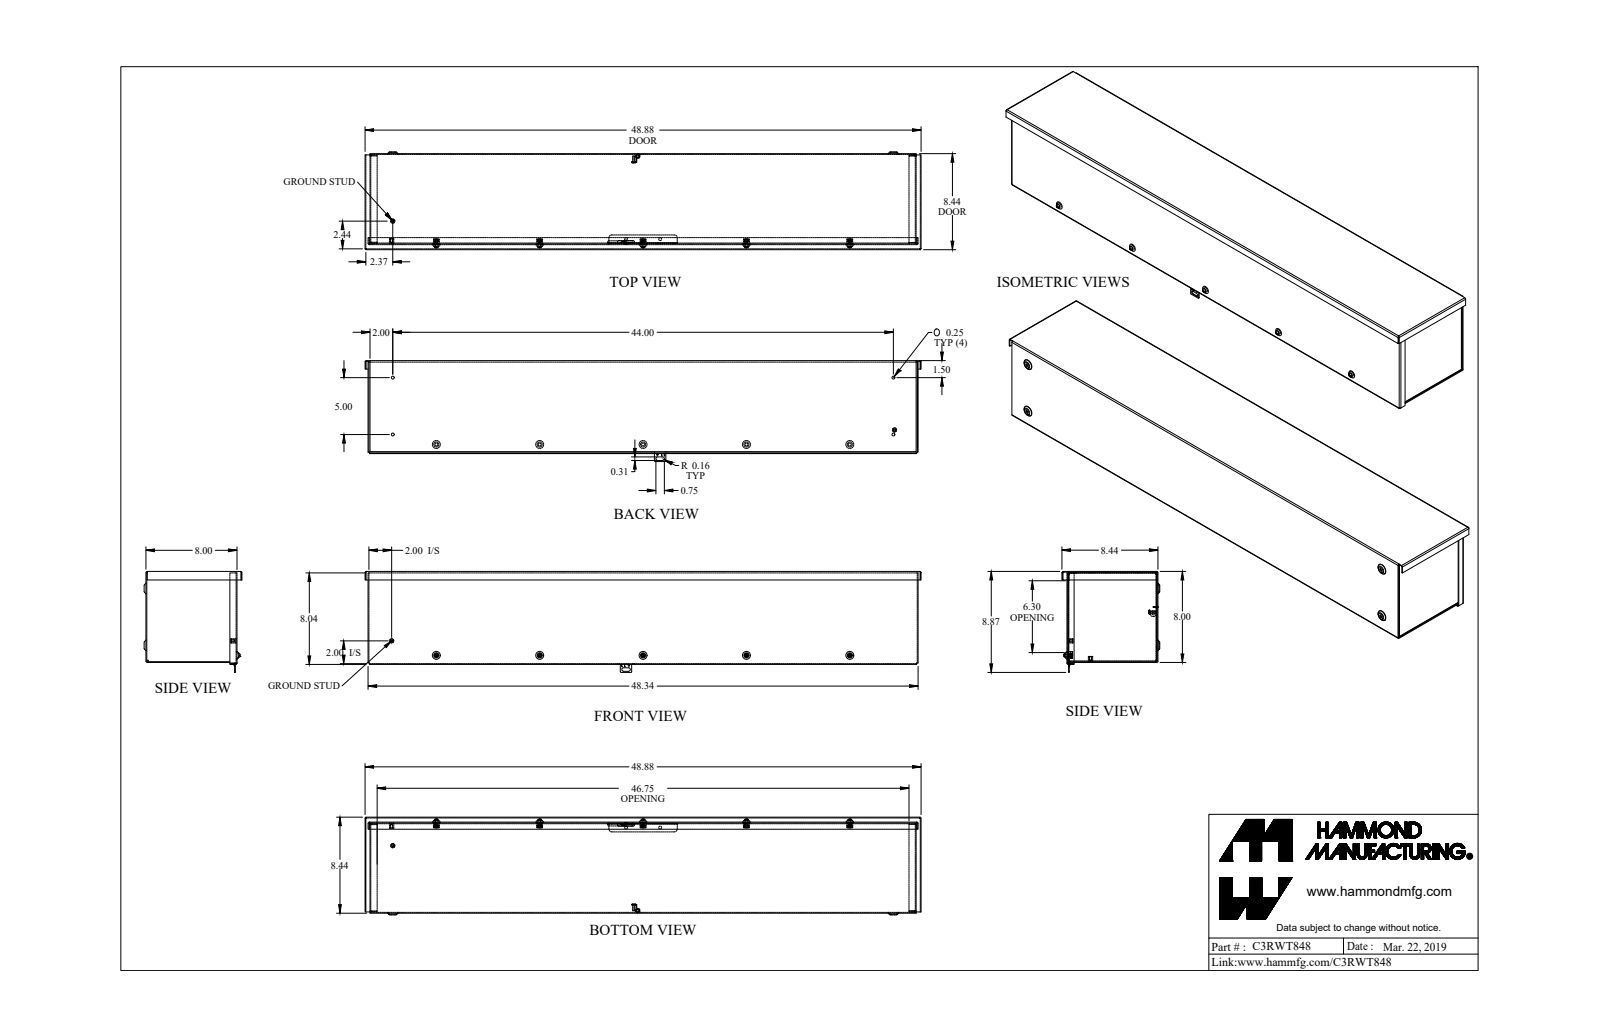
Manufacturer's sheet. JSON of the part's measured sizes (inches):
{"part_name": "C3RWT848_Default", "step_written_by": "SolidWorks 2019 (CONFIG_CONTROL_DESIGN)", "units": "inches", "bodies": {"solids": 28, "faces": 1006, "planar": 557, "cylindrical": 313, "other": 136}, "overall_size": [48.875, 8.871, 8.594], "volume_in3": 132.4, "surface_area_in2": 3715, "round_holes": [[0.156, 7], [0.25, 6], [0.214, 5], [0.23, 5], [0.203, 2], [0.125, 1], [0.137, 1], [0.2, 1], [0.215, 1]], "round_bosses_or_shafts": [[0.19, 6], [0.148, 5], [0.375, 2], [0.5, 1], [0.367, 1], [0.21, 1], [0.152, 1], [0.125, 1]], "partial_cylinders_radius": [[0.08, 20], [0.108, 20], [0.036, 18], [0.108, 18], [0.125, 13], [0.022, 10], [0.25, 6], [0.171, 5]], "face_to_face_distances": [0.072, 7.928, 7.856, 8, 47.928, 0.172, 8.366, 0.51, 0.438, 48], "hole_center_spacings": [9.086, 18.172, 9.086, 7.352, 15.67, 22.017, 22.771, 27.258]}
